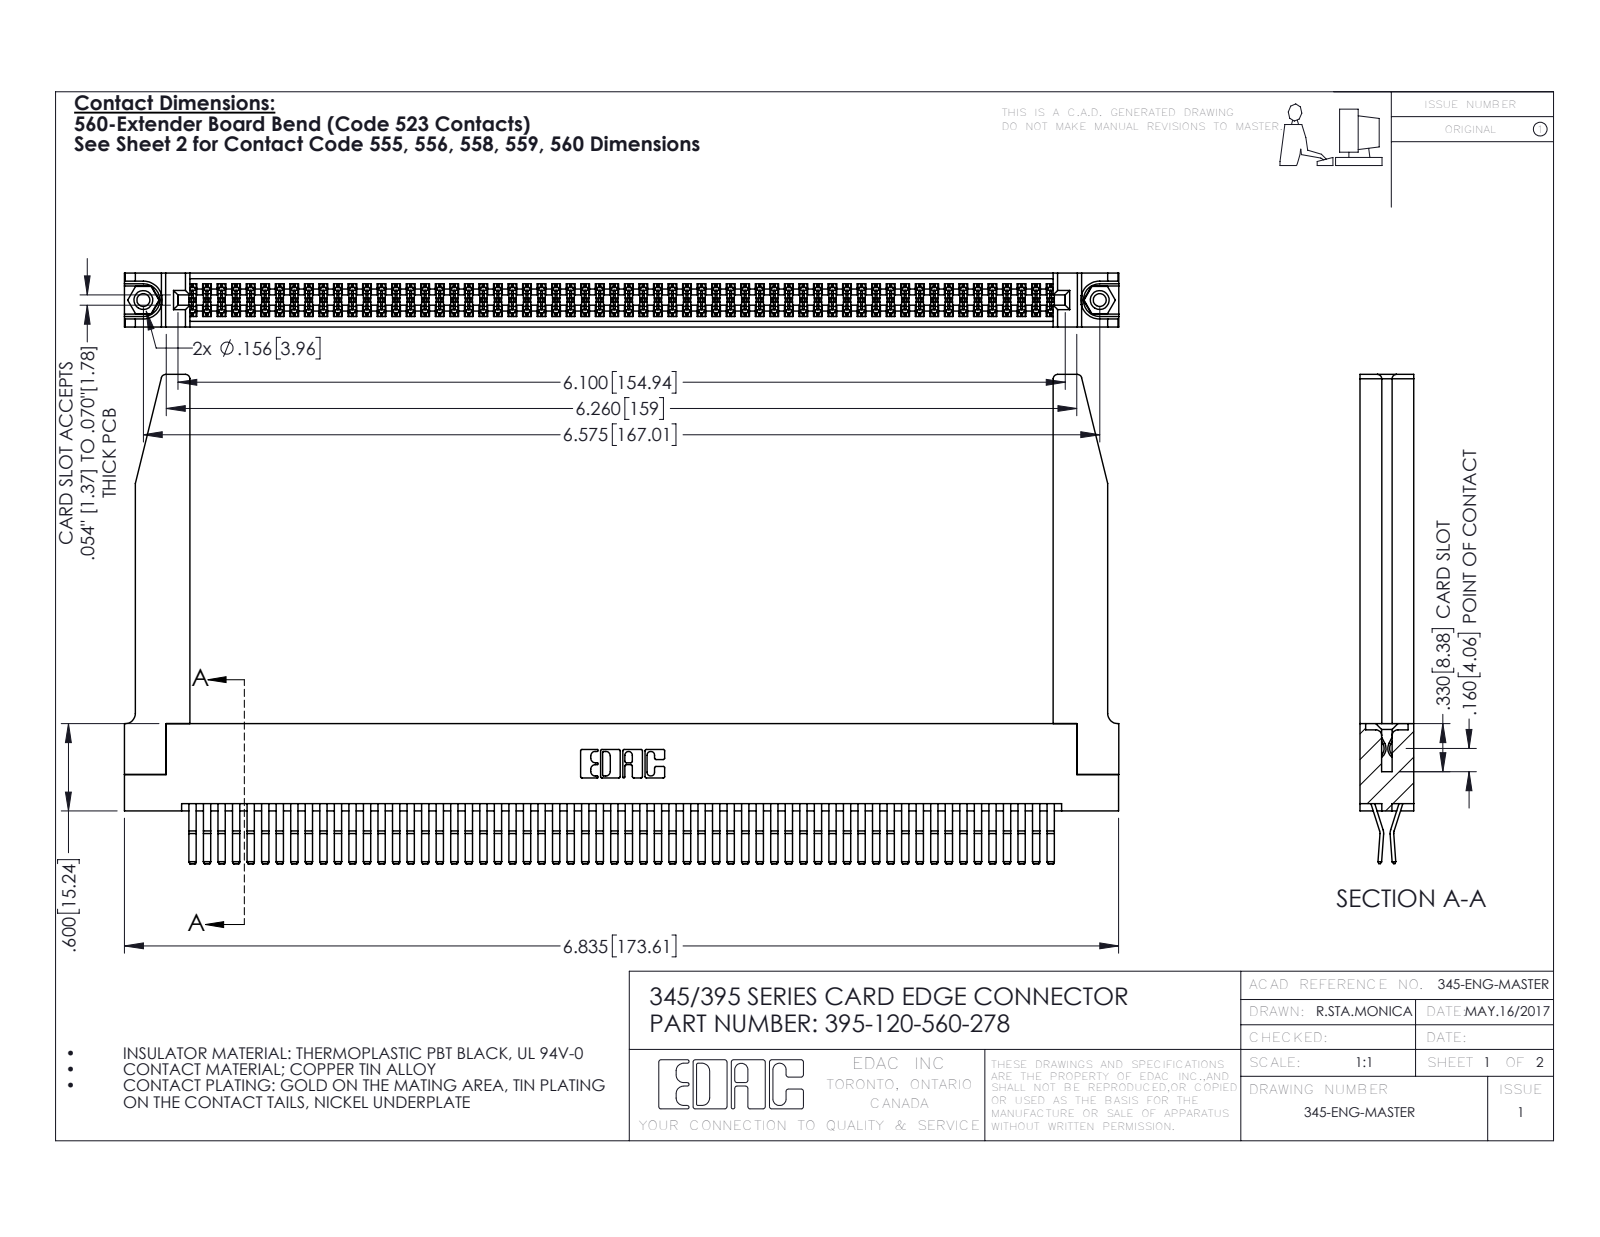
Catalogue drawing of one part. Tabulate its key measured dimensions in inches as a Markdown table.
| quantity | value |
| --- | --- |
| part name | 345-292-001_560 Tail; 345 Part_Flush Mounting Lugs - 0.156 Dia-TH; 345-250-001_345-250-001-102; 345-220-078_345-220-078 (+1 more) |
| STEP written by | SolidWorks 2016 (CONFIG_CONTROL_DESIGN) |
| units | inches |
| bodies | 125 solids, 6600 faces (4182 planar, 2366 cylindrical, 52 other) |
| overall size | 6.836 × 3.362 × 0.37 |
| volume | 1.562 in³ |
| surface area | 55.11 in² |
| round holes (diameter × count) | 0.089 × 2, 0.125 × 2, 0.156 × 2, 0.064 × 1 |
| round bosses / shafts (diameter × count) | 0.155 × 2 |
| partial cylindrical surfaces (radius × count) | 0.006 × 180, 0.01 × 22, 0.03 × 8, 0.007 × 6, 0.031 × 6, 0.026 × 3, 0.01 × 2, 0.014 × 2 |
| main face-to-face distances | 0.072, 0.37, 0.298, 0.025, 0.2, 0.098, 0.272, 0.225, 0.175, 0.148 |
| hole center spacings | 0.27, 6.339, 6.575 |
